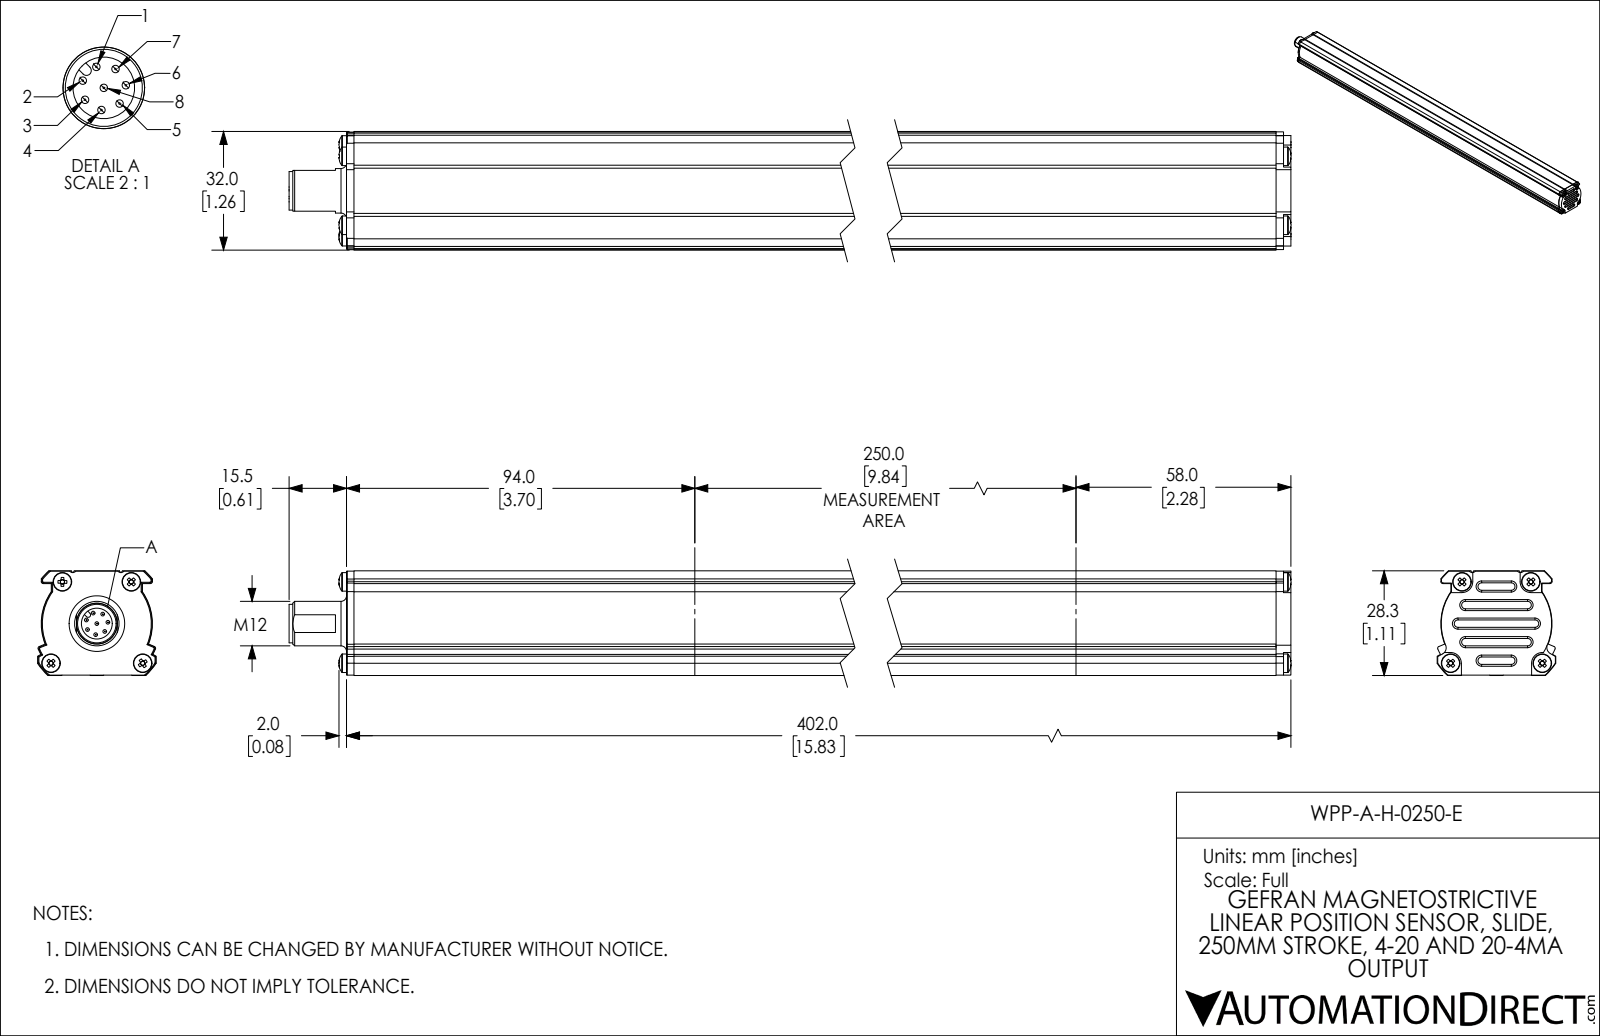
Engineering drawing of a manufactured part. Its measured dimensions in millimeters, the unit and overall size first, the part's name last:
Units: millimetres
Overall size (bounding box): 417.6 × 32 × 28.2
Round holes (diameter × count): ⌀2.3 ×4, ⌀2.6 ×4, ⌀7 ×1, ⌀8.3 ×1, ⌀9.4 ×1
Round bosses / shafts (diameter × count): ⌀1 ×8, ⌀5 ×4, ⌀12 ×1, ⌀10.4 ×1, ⌀9.6 ×1, ⌀8 ×1
Partial cylindrical surfaces — rounded edges, fillets, slot ends (radius × count): R0.5 ×8, R2.9 ×4, R0.4 ×2, R1 ×2, R1.9 ×2, R0.7 ×1, R2 ×1, R14.9 ×1
Main face-to-face distances: 28, 28.2, 24.8, 24.6, 3.5, 396, 3.7, 28.3, 2, 398
Hole centre spacings: 14.6, 16.4, 18.6, 22.1, 22.2, 24.7, 30.8, 30.9
Volume: 321 000 mm³ · Surface area: 68 900 mm²
Bodies: 20 solids, 573 faces (301 planar, 131 cylindrical, 141 other)
Part name (STEP PRODUCT): WPP-A-H-0250-E
STEP written by: SolidWorks 2021 (CONFIG_CONTROL_DESIGN)
